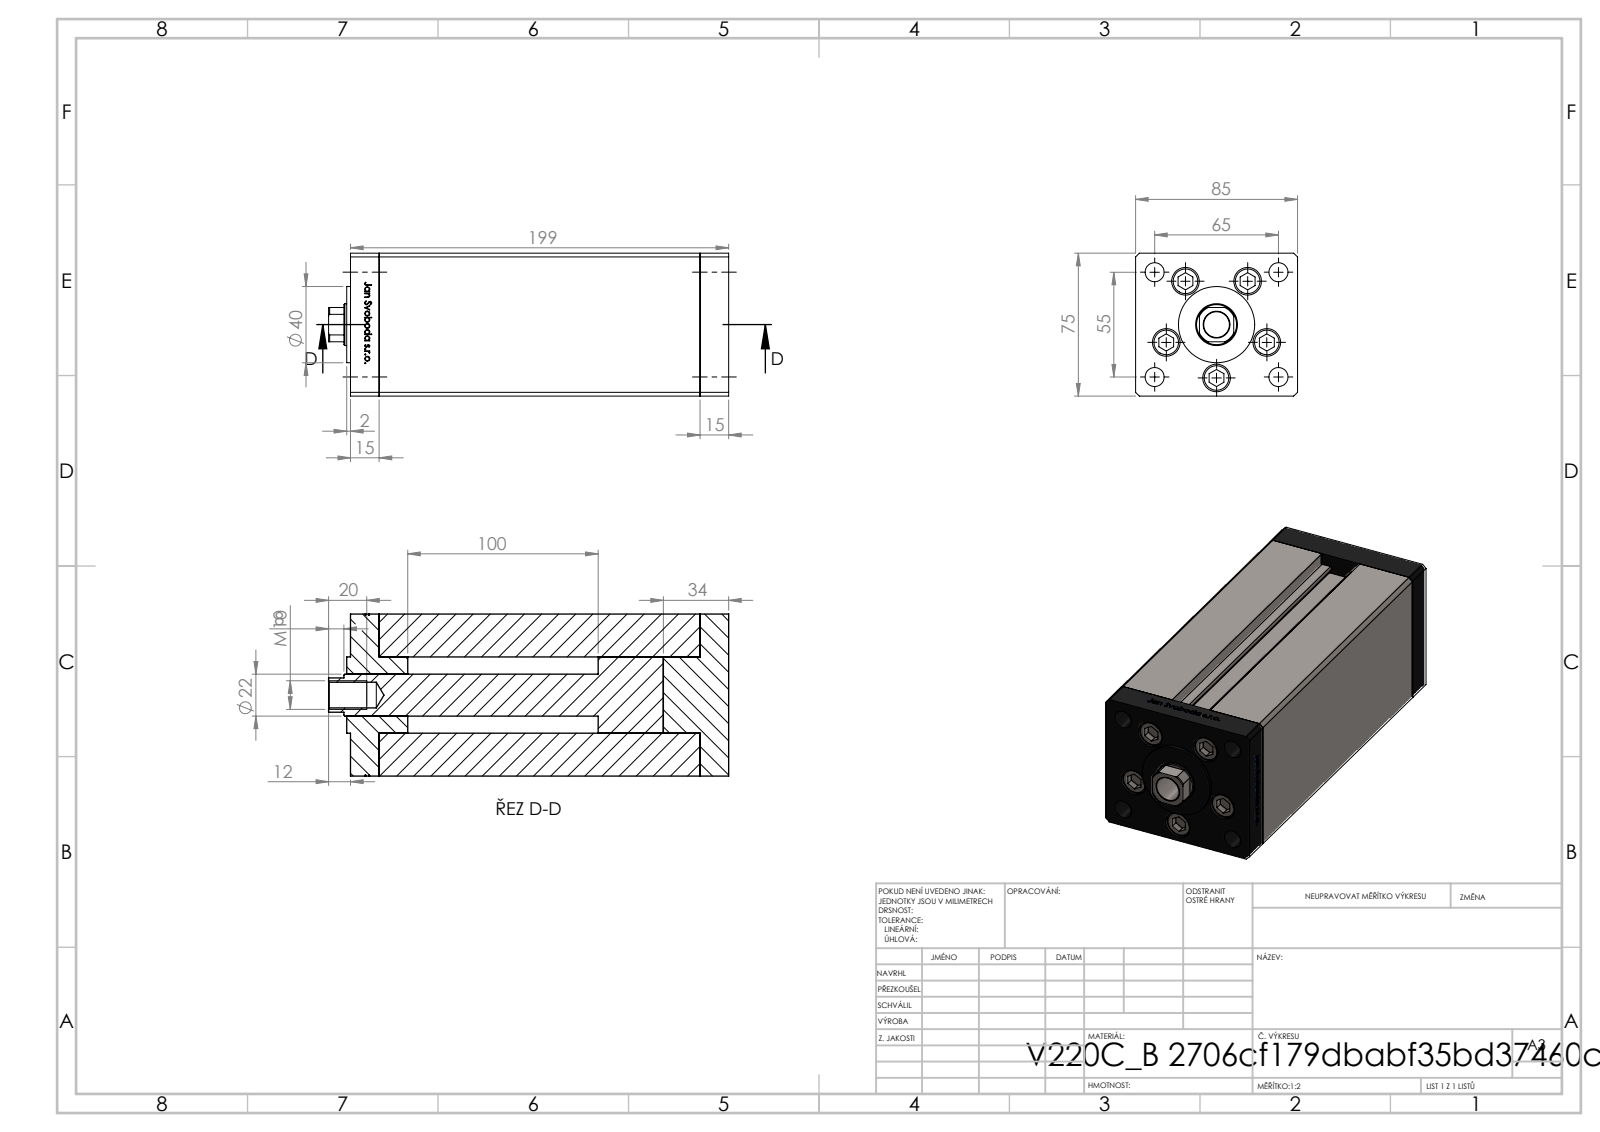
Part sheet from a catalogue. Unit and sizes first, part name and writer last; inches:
Units: inches
Overall size (bounding box): 8.268 × 3.346 × 2.953
Round holes (diameter × count): ⌀0.433 ×5, ⌀0.571 ×5, ⌀0.394 ×4, ⌀0.079 ×2, ⌀0.518 ×2, ⌀0.531 ×1, ⌀0.866 ×1
Round bosses / shafts (diameter × count): ⌀0.315 ×5, ⌀1.575 ×1
Partial cylindrical surfaces — rounded edges, fillets, slot ends (radius × count): R0.037 ×2, R0.413 ×1
Main face-to-face distances: 3.346, 2.953, 0.591, 6.634, 7.224, 7.815, 1.348, 2.697, 0.758, 5.876
Hole centre spacings: 1.102, 1.676, 0.664, 0.755, 1.273, 1.28, 1.324, 1.47
Volume: 68.22 in³ · Surface area: 265.3 in²
Bodies: 14 solids, 1185 faces (464 planar, 147 cylindrical, 574 other)
Part name (STEP PRODUCT): V220C_B MIDDLE; V220C_FRONT_B; V220C_VC_B; V220C BACK_B (+1 more)
STEP written by: SolidWorks 2019 (CONFIG_CONTROL_DESIGN)
